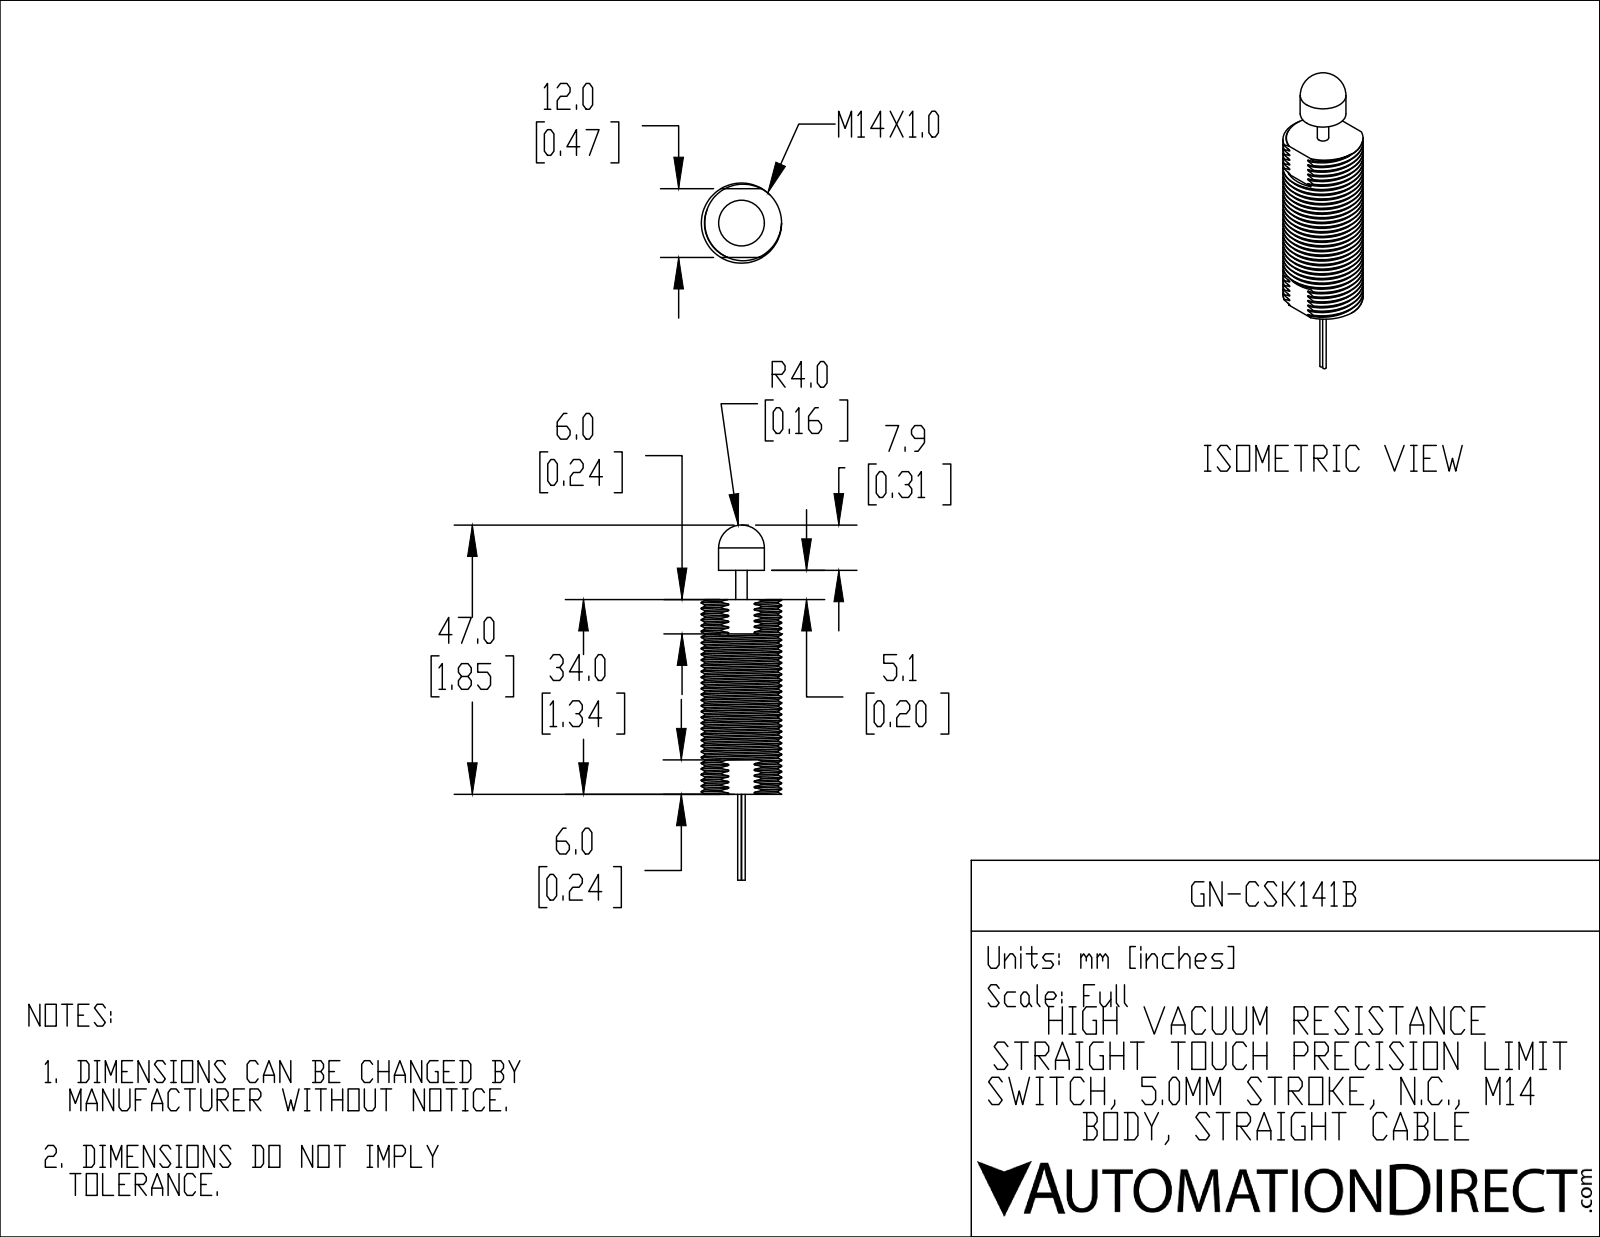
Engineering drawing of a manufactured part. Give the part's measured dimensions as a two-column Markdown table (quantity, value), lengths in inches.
| quantity | value |
| --- | --- |
| part name | GN-CSK141B |
| STEP written by | SolidWorks 2019 (AUTOMOTIVE_DESIGN) |
| units | inches |
| bodies | 1 solid, 118 faces (13 planar, 31 cylindrical, 74 other) |
| overall size | 2.441 × 0.551 × 0.551 |
| volume | 0.309 in³ |
| surface area | 4.503 in² |
| round bosses / shafts (diameter × count) | 0.024 × 2, 0.551 × 1, 0.315 × 1, 0.079 × 1 |
| partial cylindrical surfaces (radius × count) | 0.508 × 1, 0.544 × 1 |
| main face-to-face distances | 1.339, 0.472, 0.201, 1.539, 0.236, 1.102, 0.437, 1.303, 0.866, 2.13 |
